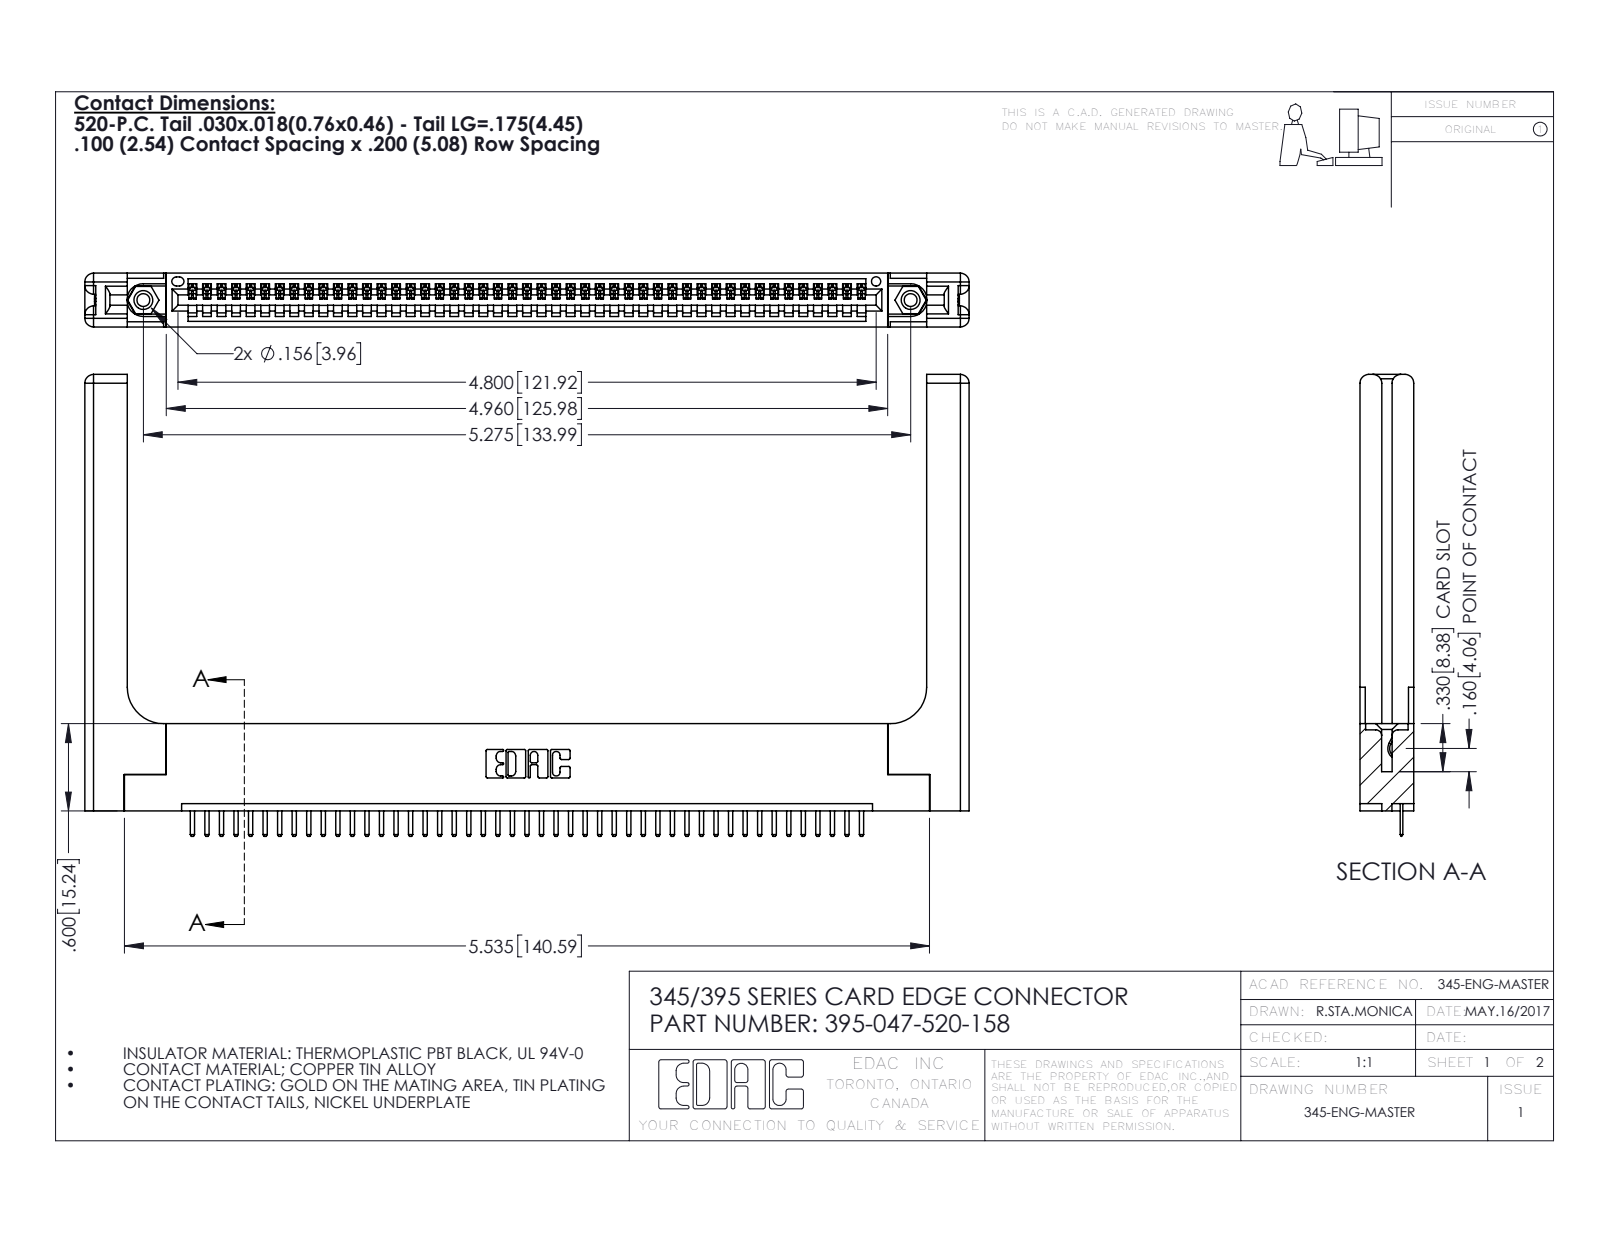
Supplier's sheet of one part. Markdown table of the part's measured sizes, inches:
| quantity | value |
| --- | --- |
| part name | 345-292-001_345-293-120; 345 Part_Flush Mounting Lugs - 0.156 Dia-TH; 395-047-520-158; 345-220-058_345-220-058 (+1 more) |
| STEP written by | SolidWorks 2016 (CONFIG_CONTROL_DESIGN) |
| units | inches |
| bodies | 52 solids, 3296 faces (2202 planar, 1034 cylindrical, 60 other) |
| overall size | 6.079 × 3.175 × 0.37 |
| volume | 1.408 in³ |
| surface area | 37.66 in² |
| round holes (diameter × count) | 0.089 × 2, 0.125 × 2, 0.156 × 2, 0.064 × 1 |
| round bosses / shafts (diameter × count) | 0.155 × 2 |
| partial cylindrical surfaces (radius × count) | 0.01 × 96, 0.006 × 94, 0.01 × 22, 0.06 × 16, 0.007 × 6, 0.031 × 6, 0.026 × 3, 0.03 × 2 |
| main face-to-face distances | 0.37, 0.072, 0.298, 0.2, 0.098, 0.272, 0.025, 0.225, 0.148, 0.15 |
| hole center spacings | 0.27, 5.039, 5.275 |
